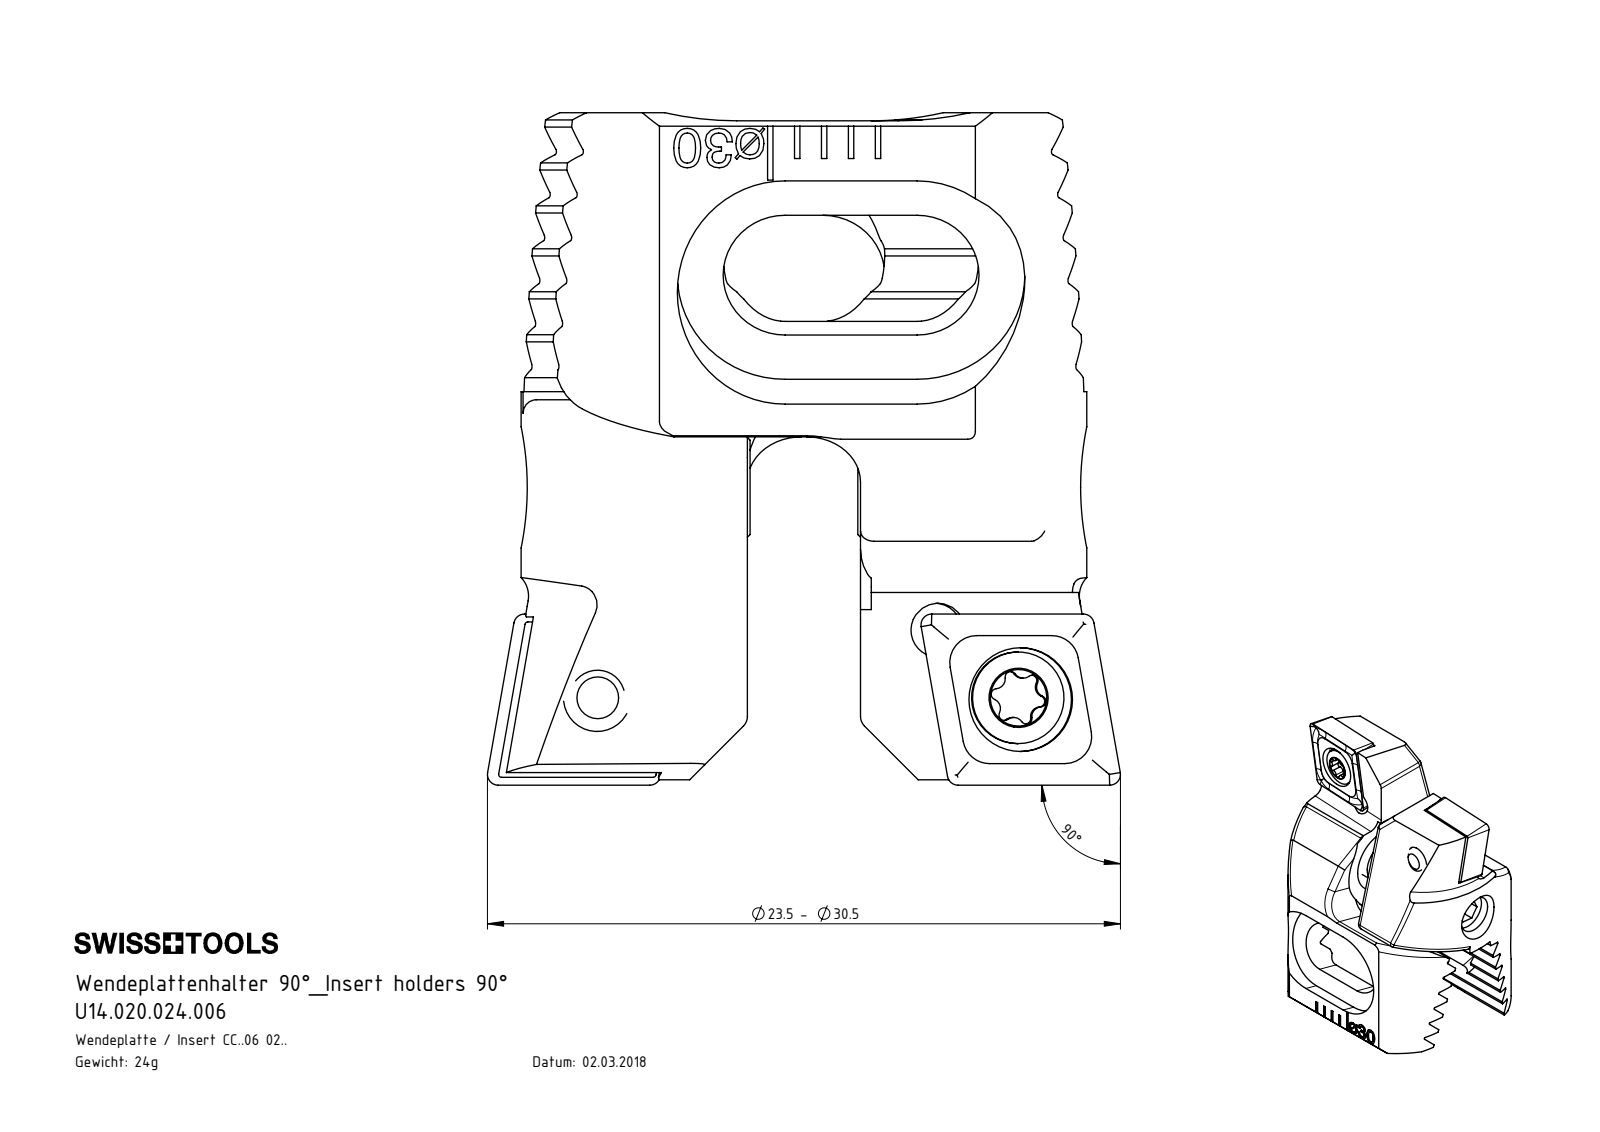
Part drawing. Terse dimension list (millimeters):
name: WCA-ER2.001.006_A; Z20-xxx.001.015_D; Z20.WCA.B11.015; Z20-ER3.001.007_A (+1 more)
written by: SolidWorks 2017 (AUTOMOTIVE_DESIGN)
unit: mm
bodies: 8 solids, 538 faces (262 planar, 104 cylindrical, 172 other)
size: 24.95 × 23.5 × 16.2
volume: 2 962 mm³; area: 3 413 mm²
holes: 2× ⌀1.6, 2× ⌀2, 2× ⌀2.05, 2× ⌀2.8, 2× ⌀3.85, 1× ⌀3.5, 1× ⌀9.1
bosses: 2× ⌀3.4, 2× ⌀2.5, 1× ⌀4
rounds: 16× R0.5, 12× R0.12, 12× R0.21, 10× R0.36, 4× R1, 4× R2, 4× R2.3, 4× R4
face distances: 1.43, 2.86, 4.29, 3.79, 0.4, 4.6, 5.71, 5.72, 2.97, 6.76
hole spacings: 3.91, 4.01, 5.5, 13.15, 13.24, 15.98, 9.91, 10.62
